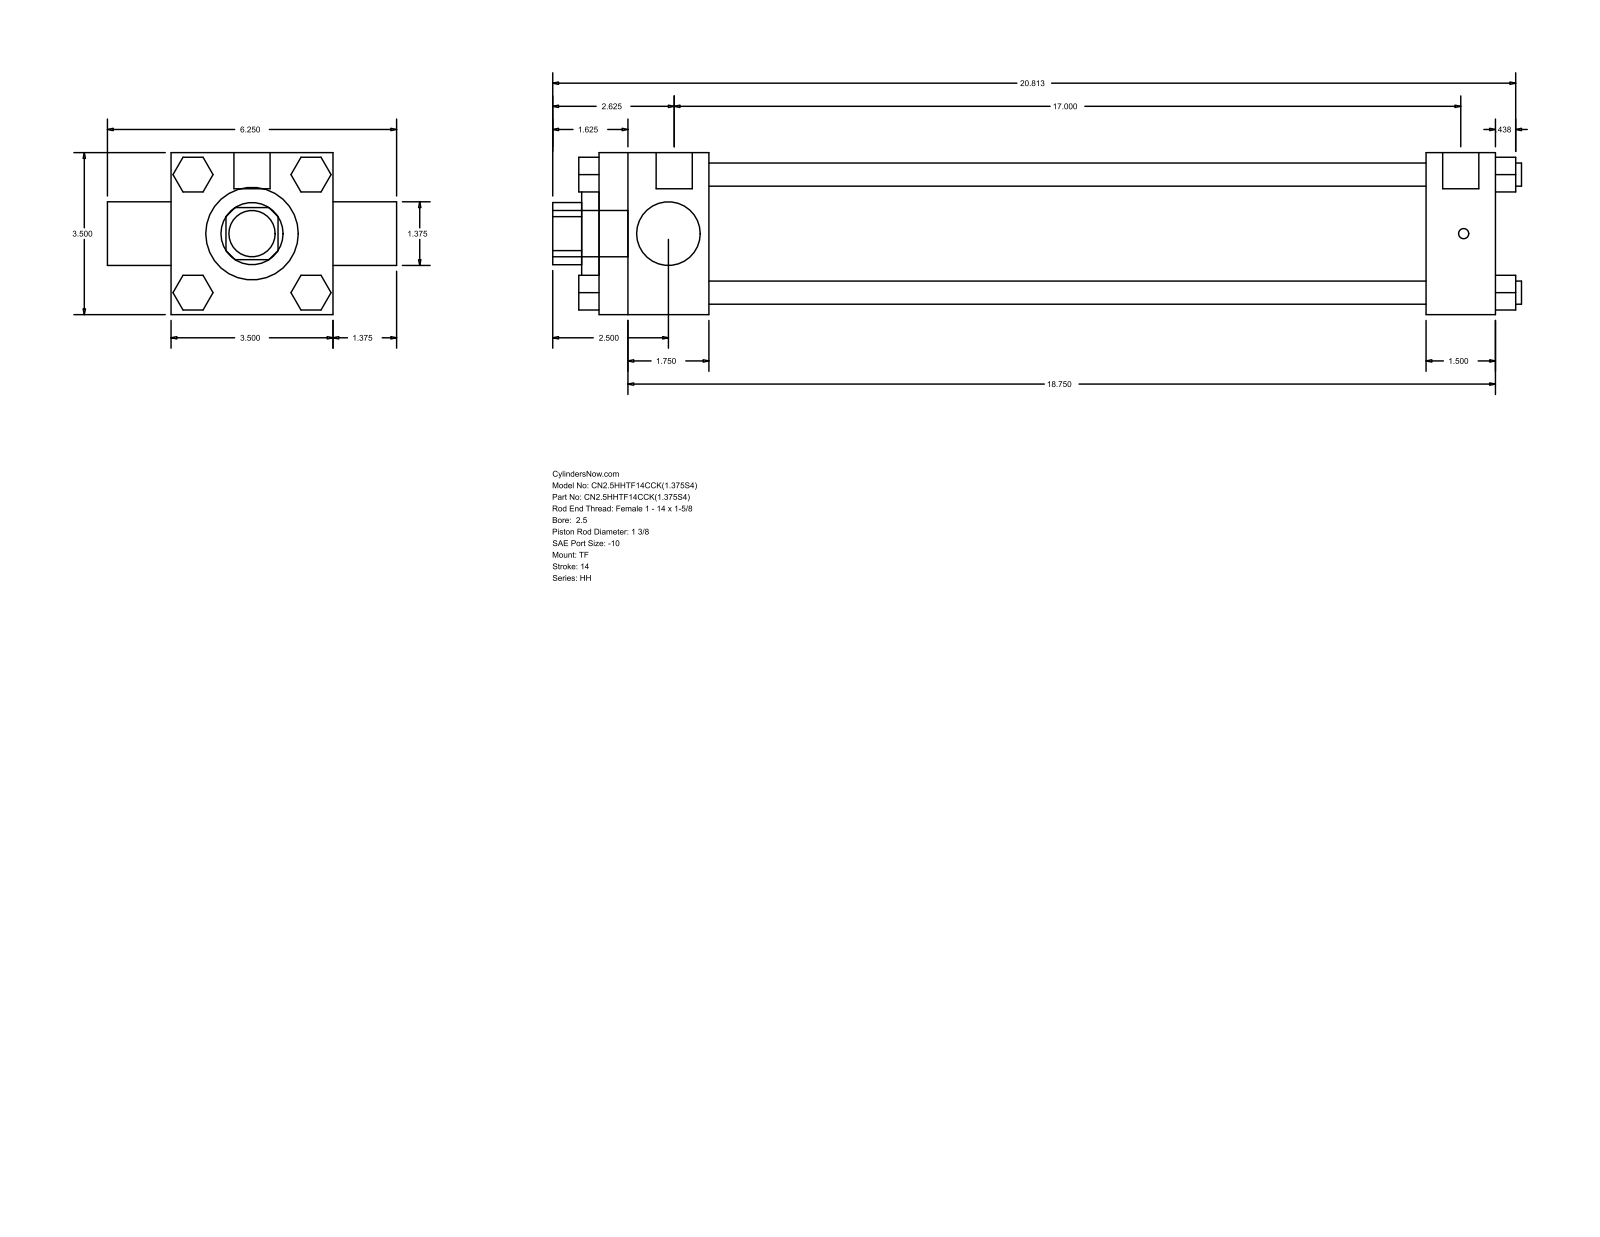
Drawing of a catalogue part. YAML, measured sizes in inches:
part_name: "HH_TF__0250_1.375"
step_written_by: "GSSL Pune (CONFIG_CONTROL_DESIGN)"
units: inches
bodies: {solids: 0, faces: 120, planar: 92, cylindrical: 28, other: 0}
overall_size: [20.937, 6.25, 3.5]
round_holes:
  - {diameter: 1.375, count: 2}
  - {diameter: 2, count: 1}
  - {diameter: 2.875, count: 1}
round_bosses_or_shafts:
  - {diameter: 0.5, count: 4}
  - {diameter: 0.219, count: 3}
  - {diameter: 0.781, count: 2}
  - {diameter: 1, count: 1}
partial_cylinders:
  - {radius: 0.672, count: 1}
face_to_face_distances: [3.5, 19.375, 2.375, 17, 17.875, 15.5, 1.5, 0.75, 1.275, 2.208]
